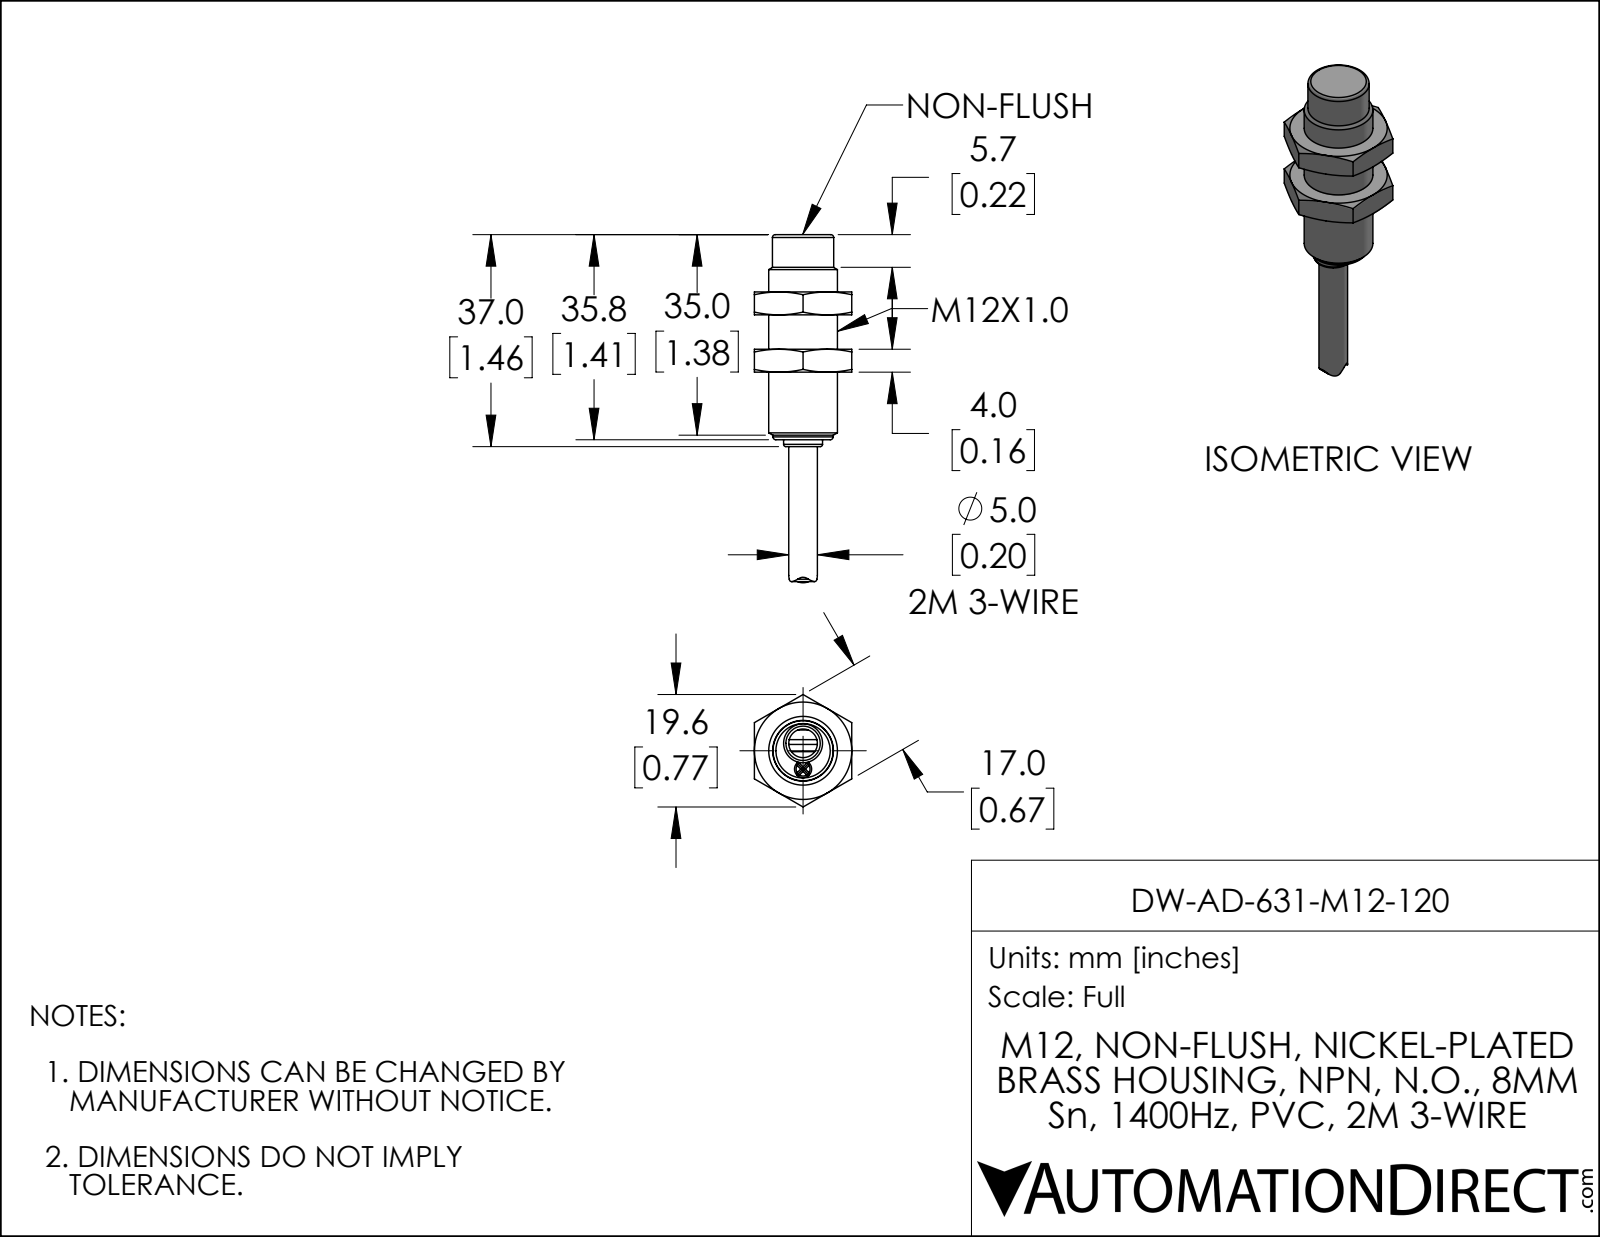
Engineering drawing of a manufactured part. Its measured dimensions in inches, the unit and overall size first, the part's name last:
Units: inches
Overall size (bounding box): 2.392 × 0.773 × 0.669
Round bosses / shafts (diameter × count): ⌀0.472 ×1, ⌀0.421 ×1, ⌀0.413 ×1, ⌀0.268 ×1, ⌀0.197 ×1, ⌀0.118 ×1
Partial cylindrical surfaces — rounded edges, fillets, slot ends (radius × count): R0.031 ×1, R0.041 ×1, R0.165 ×1, R0.248 ×1, R0.331 ×1
Main face-to-face distances: 0.394, 0.157, 0.669, 0.551, 0.236, 0.787, 0.945, 1.409, 1.016, 0.858
Volume: 0.333 in³ · Surface area: 4.025 in²
Bodies: 1 solid, 80 faces (33 planar, 13 cylindrical, 34 other)
Part name (STEP PRODUCT): DW-AD-631-M12-120
STEP written by: SolidWorks 2019 (AUTOMOTIVE_DESIGN)
